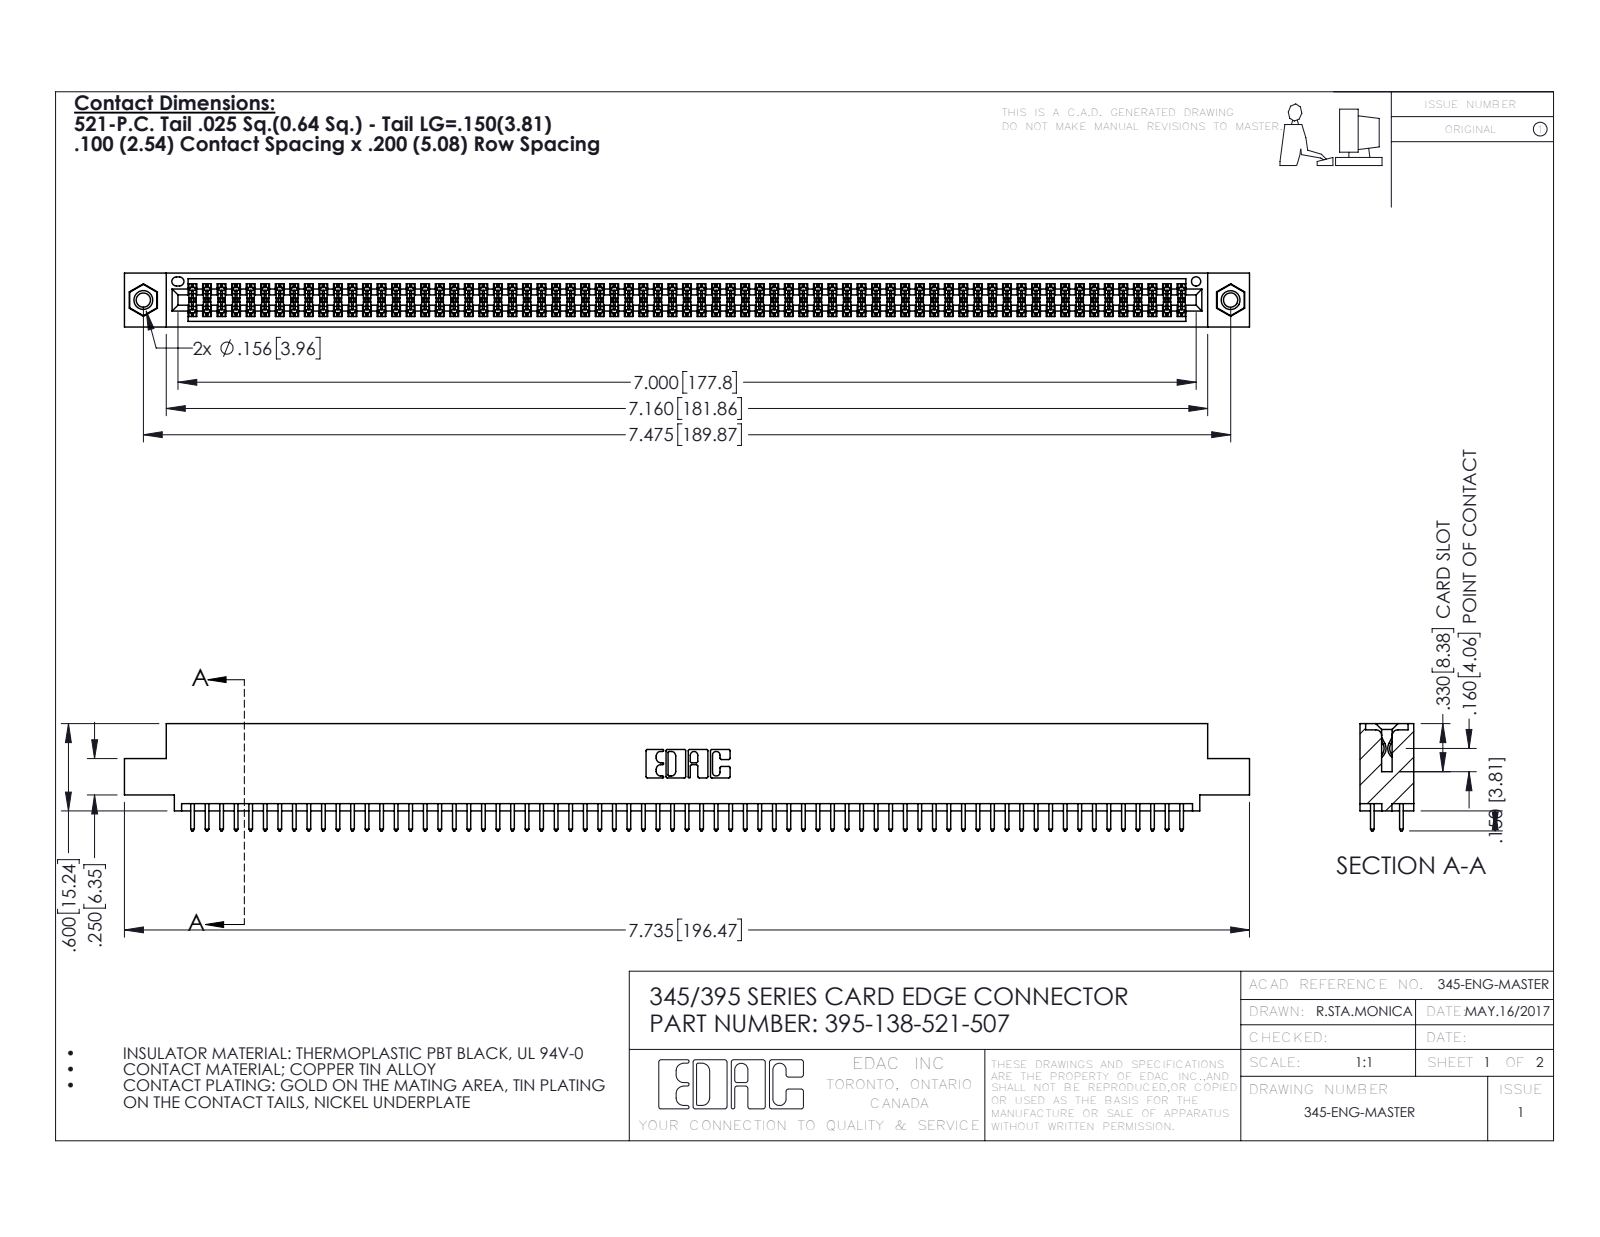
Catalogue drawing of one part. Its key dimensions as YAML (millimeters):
part_name: "345 Part_0.110 Offset - 0.156 Dia-TI; 345-292-001_345-293-121; 395-138-521-507; 345-250-001_345-250-005-103"
step_written_by: "SolidWorks 2016 (CONFIG_CONTROL_DESIGN)"
units: millimeters
bodies: {solids: 141, faces: 7090, planar: 4670, cylindrical: 2404, other: 16}
overall_size: [196.5, 18.7, 9.4]
volume: 19190
surface_area: 28650
round_holes:
  - {diameter: 2.5, count: 2}
  - {diameter: 3.2, count: 2}
  - {diameter: 4, count: 2}
  - {diameter: 1.6, count: 1}
round_bosses_or_shafts:
  - {diameter: 3.9, count: 2}
partial_cylinders:
  - {radius: 0.2, count: 207}
  - {radius: 0.3, count: 138}
  - {radius: 0.3, count: 22}
  - {radius: 0.2, count: 6}
  - {radius: 0.8, count: 6}
  - {radius: 0.7, count: 3}
  - {radius: 0.4, count: 2}
  - {radius: 0.5, count: 2}
face_to_face_distances: [1.8, 7.6, 5.1, 2.5, 6.9, 0.6, 9.4, 5.7, 4.4, 3.8]
hole_center_spacings: [6.9, 183.9, 189.9]
